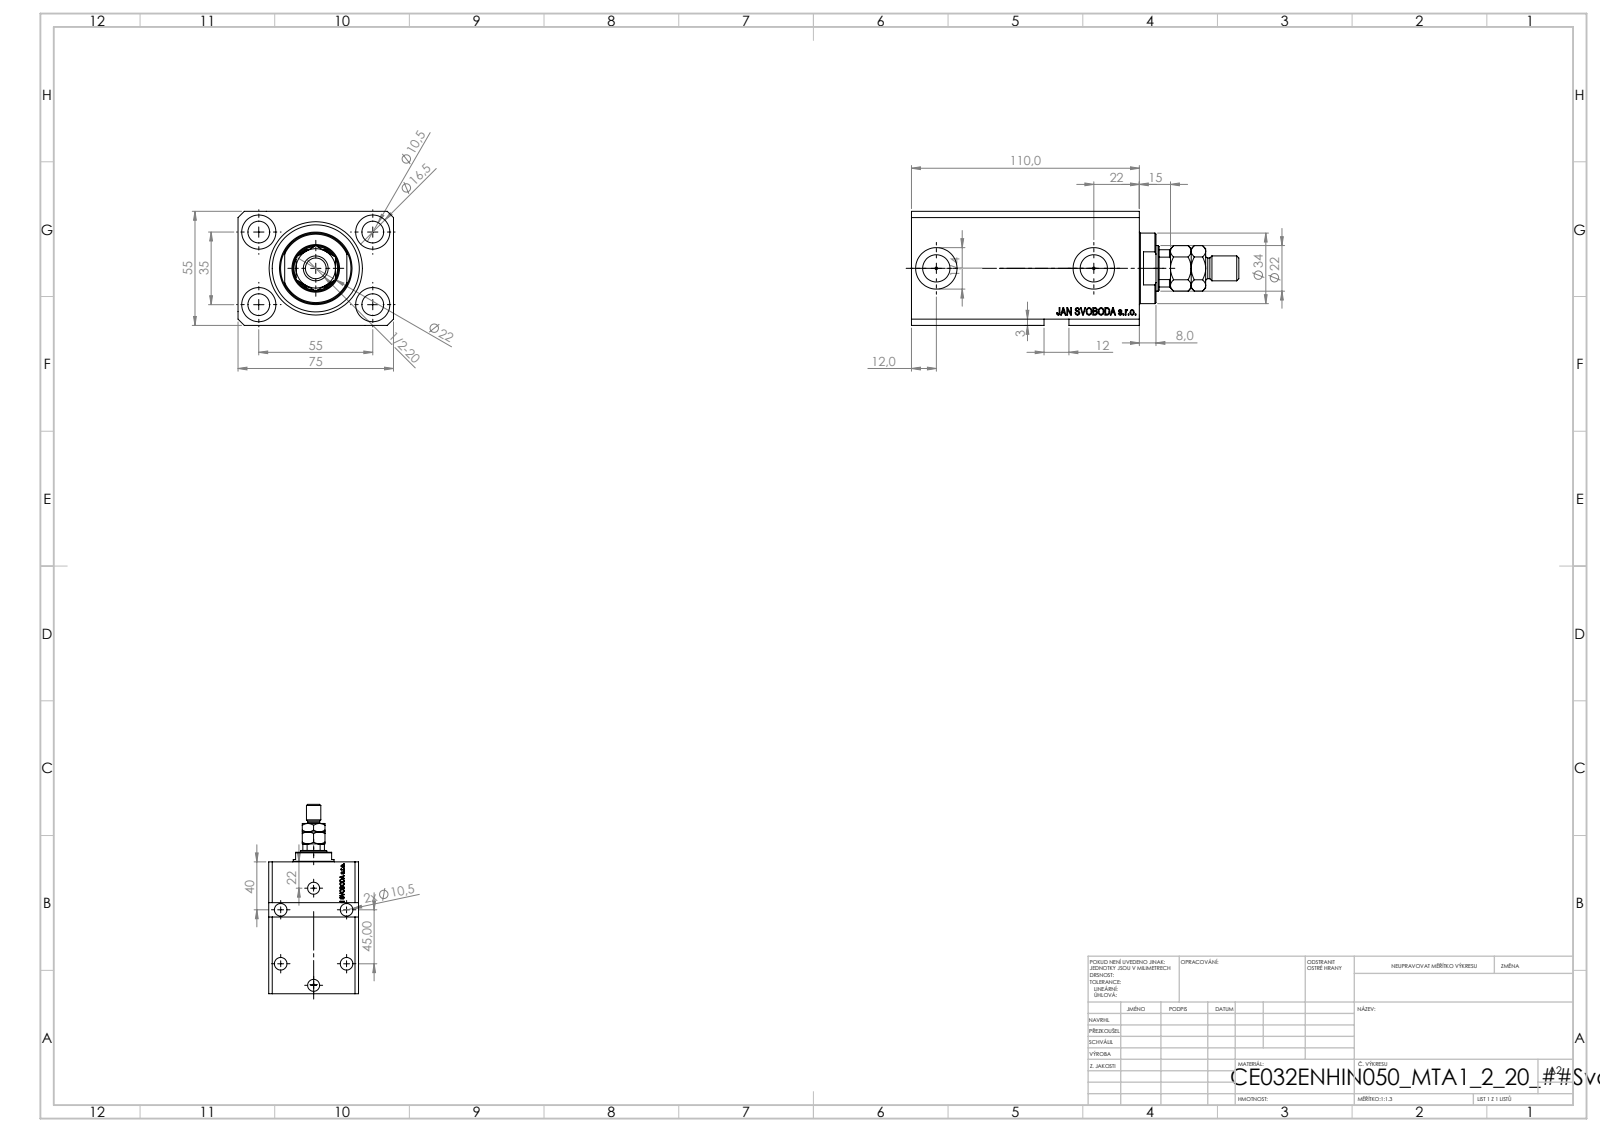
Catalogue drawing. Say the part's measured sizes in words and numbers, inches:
The part is named "V250CE_E_Body; V250CE_C_VCP; V250CE_VC_E; MTA". Its 3-D file was written by "SolidWorks 2019 (CONFIG_CONTROL_DESIGN)". It is 4 solids with 963 faces: 453 planar, 108 cylindrical and 402 other. Overall it measures 6.22 by 2.953 by 2.165 inches. Its volume is 22.95 cubic inches and its surface area 135.9 square inches. Round holes: 9 of diameter 0.413, 4 of diameter 0.049, 4 of diameter 0.65, 2 of diameter 0.394, 2 of diameter 0.518, 2 of diameter 0.787, 1 of diameter 0.866, 1 of diameter 1.26, 1 of diameter 1.772. Round bosses or shafts: 1 of diameter 1.339, 1 of diameter 0.472, 1 of diameter 0.394. Partial cylindrical surfaces (rounded edges, fillets, slot ends): 1 of radius 0.413. The main face-to-face distances are 2.165, 2.953, 0.591, 4.331, 3.74, 0.39, 3.35, 3.941, 0.748, 0.433. The hole center spacings are 1.283, 1.294, 2.165, 2.706, 1.283, 1.378, 1.772, 2.567.
